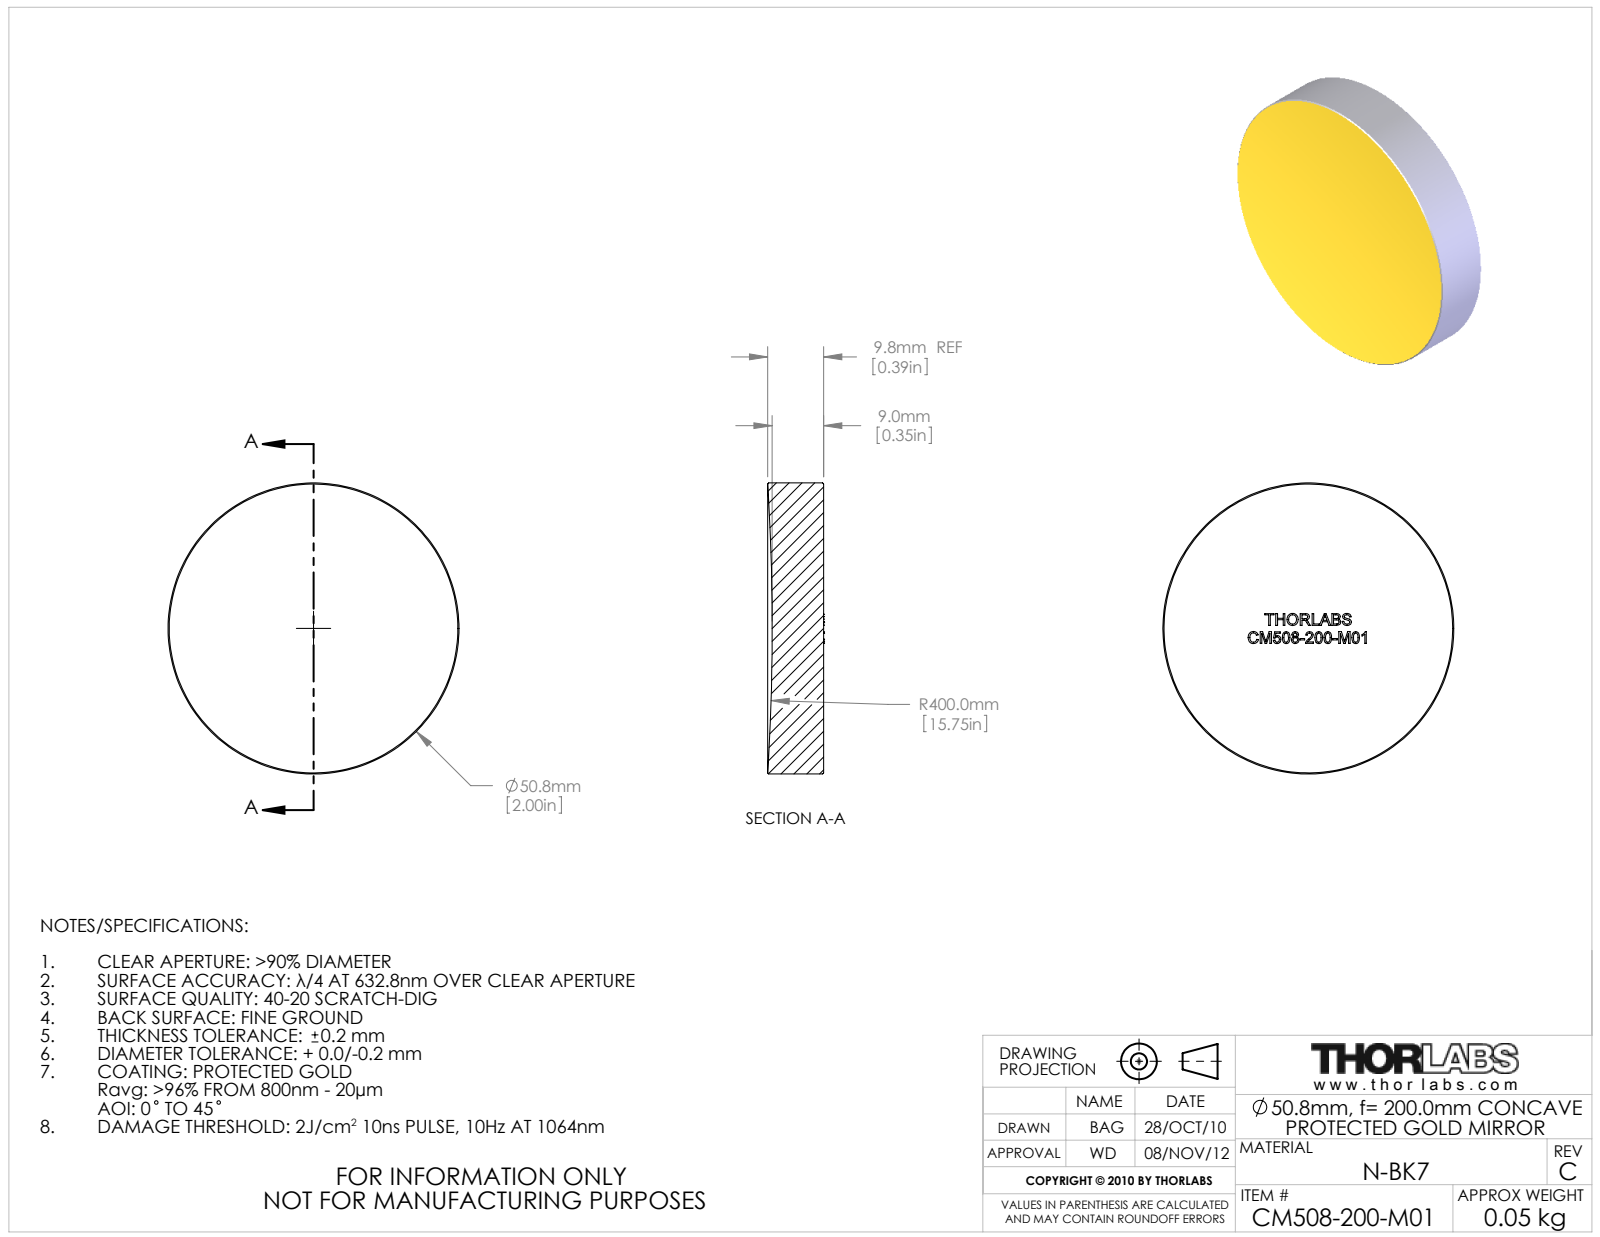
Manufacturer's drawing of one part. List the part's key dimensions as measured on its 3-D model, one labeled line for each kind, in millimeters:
Part name (STEP PRODUCT): 17589-E0W
STEP written by: SolidWorks 2009 (AUTOMOTIVE_DESIGN)
Units: millimetres
Bodies: 1 solid, 282 faces (144 planar, 2 cylindrical, 136 other)
Overall size (bounding box): 50.8 × 50.8 × 9.8
Volume: 19 060 mm³ · Surface area: 5 582 mm²
Round bosses / shafts (diameter × count): ⌀50.8 ×1
Main face-to-face distances: 2.1, 3.1, 2.5, 13.9, 3.2, 5.5, 6.3, 1, 11.4, 13.7
